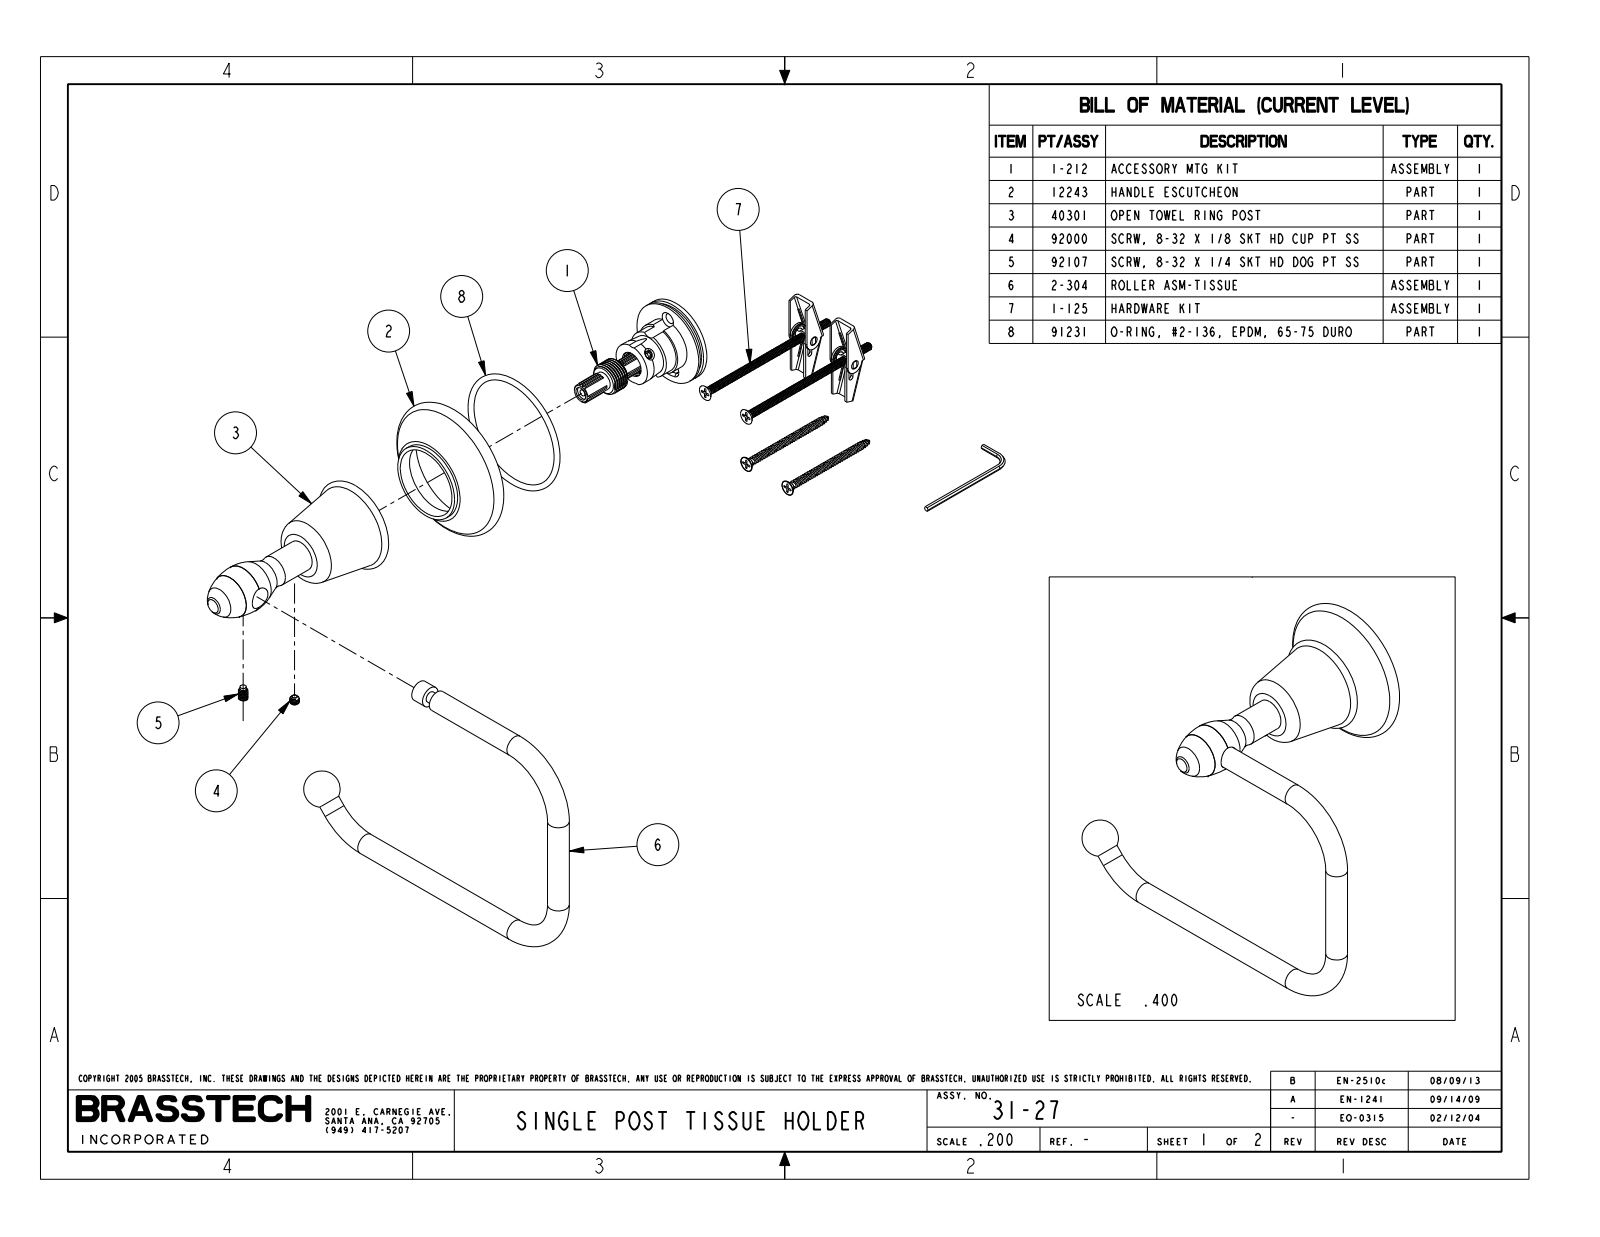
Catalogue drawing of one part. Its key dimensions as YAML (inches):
part_name: "31-27_WEB"
step_written_by: "PRO/ENGINEER BY PARAMETRIC TECHNOLOGY CORPORATION, 2009300 (CONFIG_CONTROL_DESIGN)"
units: inches
bodies: {solids: 0, faces: 87, planar: 7, cylindrical: 34, other: 46}
overall_size: [6.247, 5.238, 4.153]
round_holes:
  - {diameter: 0.136, count: 1}
round_bosses_or_shafts:
  - {diameter: 0.375, count: 4}
  - {diameter: 0.865, count: 1}
  - {diameter: 0.553, count: 1}
  - {diameter: 0.164, count: 1}
face_to_face_distances: [1.975, 0.035]
